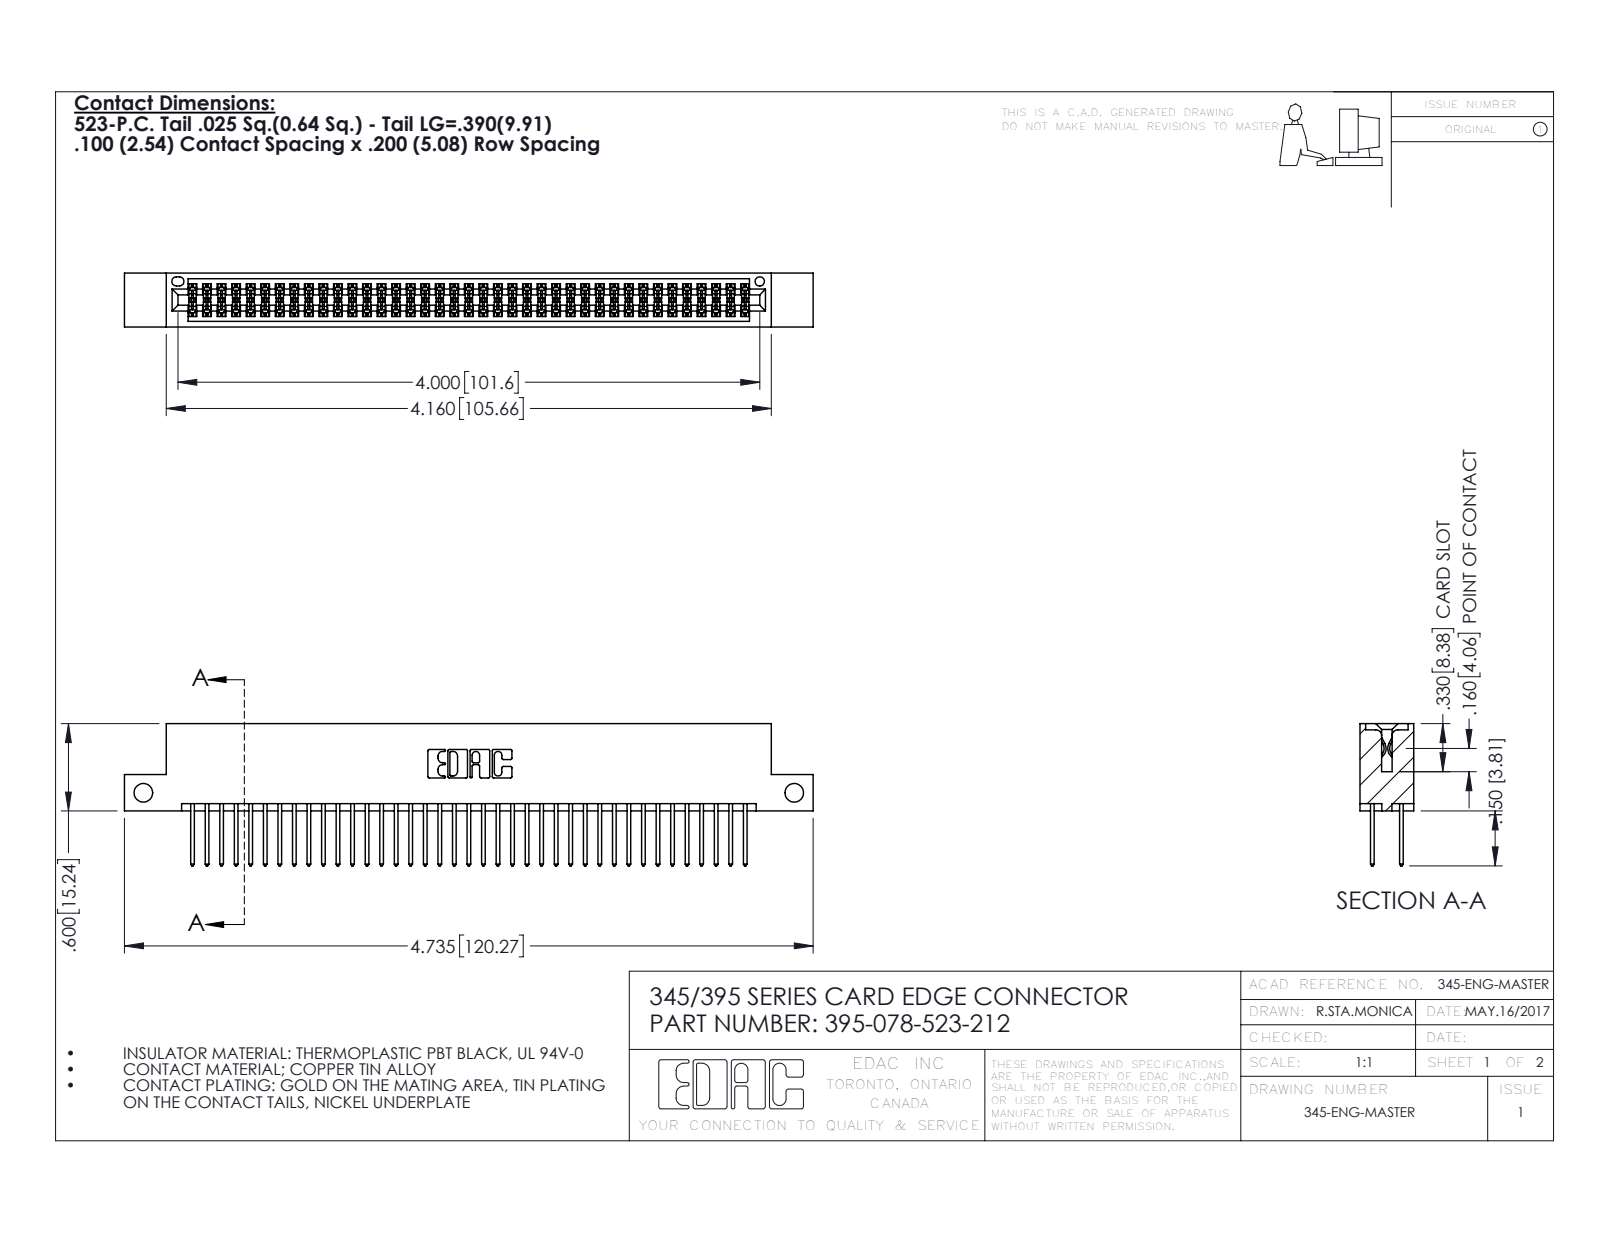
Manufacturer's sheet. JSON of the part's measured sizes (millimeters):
{"part_name": "345-292-001_345-293-123; 345 Part_Flush Mounting Lugs - Side Mount; 395-078-523-212", "step_written_by": "SolidWorks 2016 (CONFIG_CONTROL_DESIGN)", "units": "millimeters", "bodies": {"solids": 79, "faces": 4026, "planar": 2654, "cylindrical": 1372, "other": 0}, "overall_size": [120.3, 24.8, 9.4], "volume_mm3": 11700, "surface_area_mm2": 17860, "round_holes": [[3.3, 2], [1.6, 1]], "partial_cylinders_radius": [[0.2, 117], [0.3, 78], [0.3, 22], [0.2, 6], [0.8, 6], [0.7, 3], [0.4, 2], [0.5, 2]], "face_to_face_distances": [7.6, 1.8, 5.1, 2.5, 6.9, 0.6, 9.4, 5.7, 4.4, 3.8], "hole_center_spacings": [113.7]}
